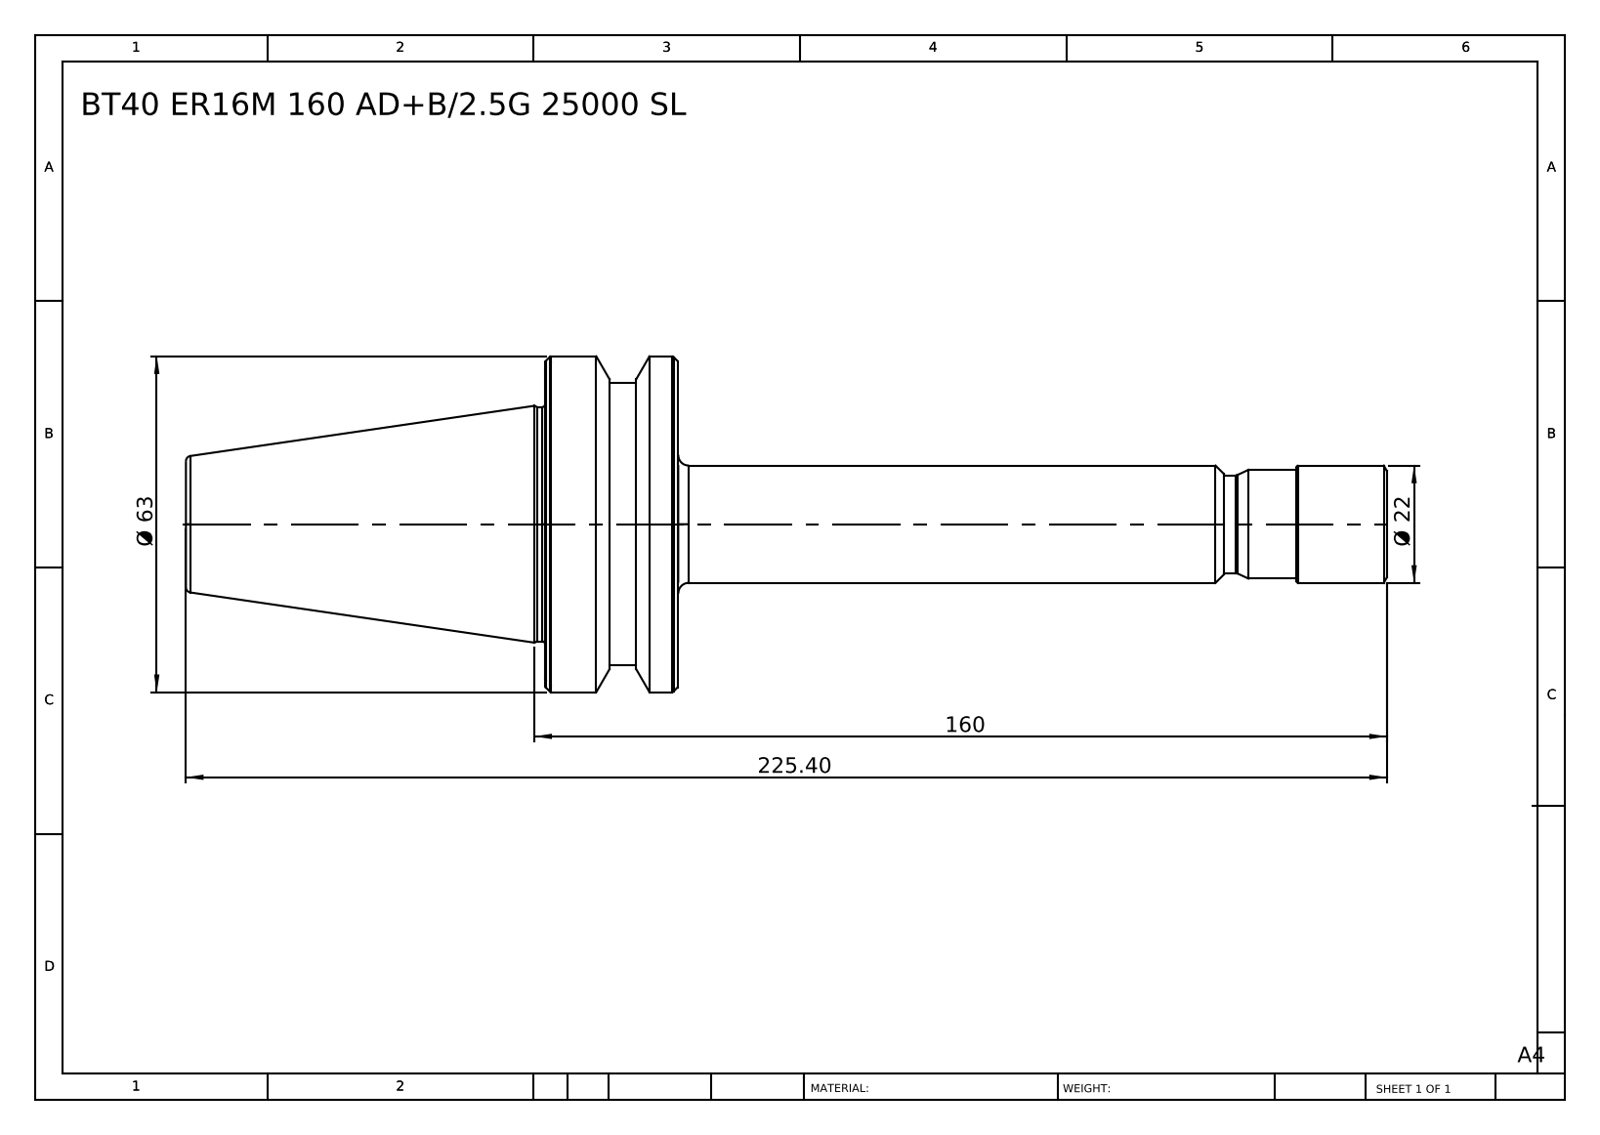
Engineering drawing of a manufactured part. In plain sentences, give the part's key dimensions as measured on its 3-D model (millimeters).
The part is named "BT40 ER16M 160 AD+B-2.5G 25000 SL". Its 3-D file was written by "SolidWorks 2014 (CONFIG_CONTROL_DESIGN)". It is 1 solid with 66 faces: 8 planar, 16 cylindrical and 42 other. Overall it measures 225.4 by 63 by 63 millimeters. Its volume is 187 996 cubic millimeters and its surface area 27 438 square millimeters. Round bosses or shafts: 1 of diameter 63, 1 of diameter 53, 1 of diameter 44, 1 of diameter 22, 1 of diameter 20.4, 1 of diameter 18.4. The main face-to-face distances are 25, 92.4, 67.4, 133, 158, 225.4, 145.9, 12.9, 12.1, 79.5.
